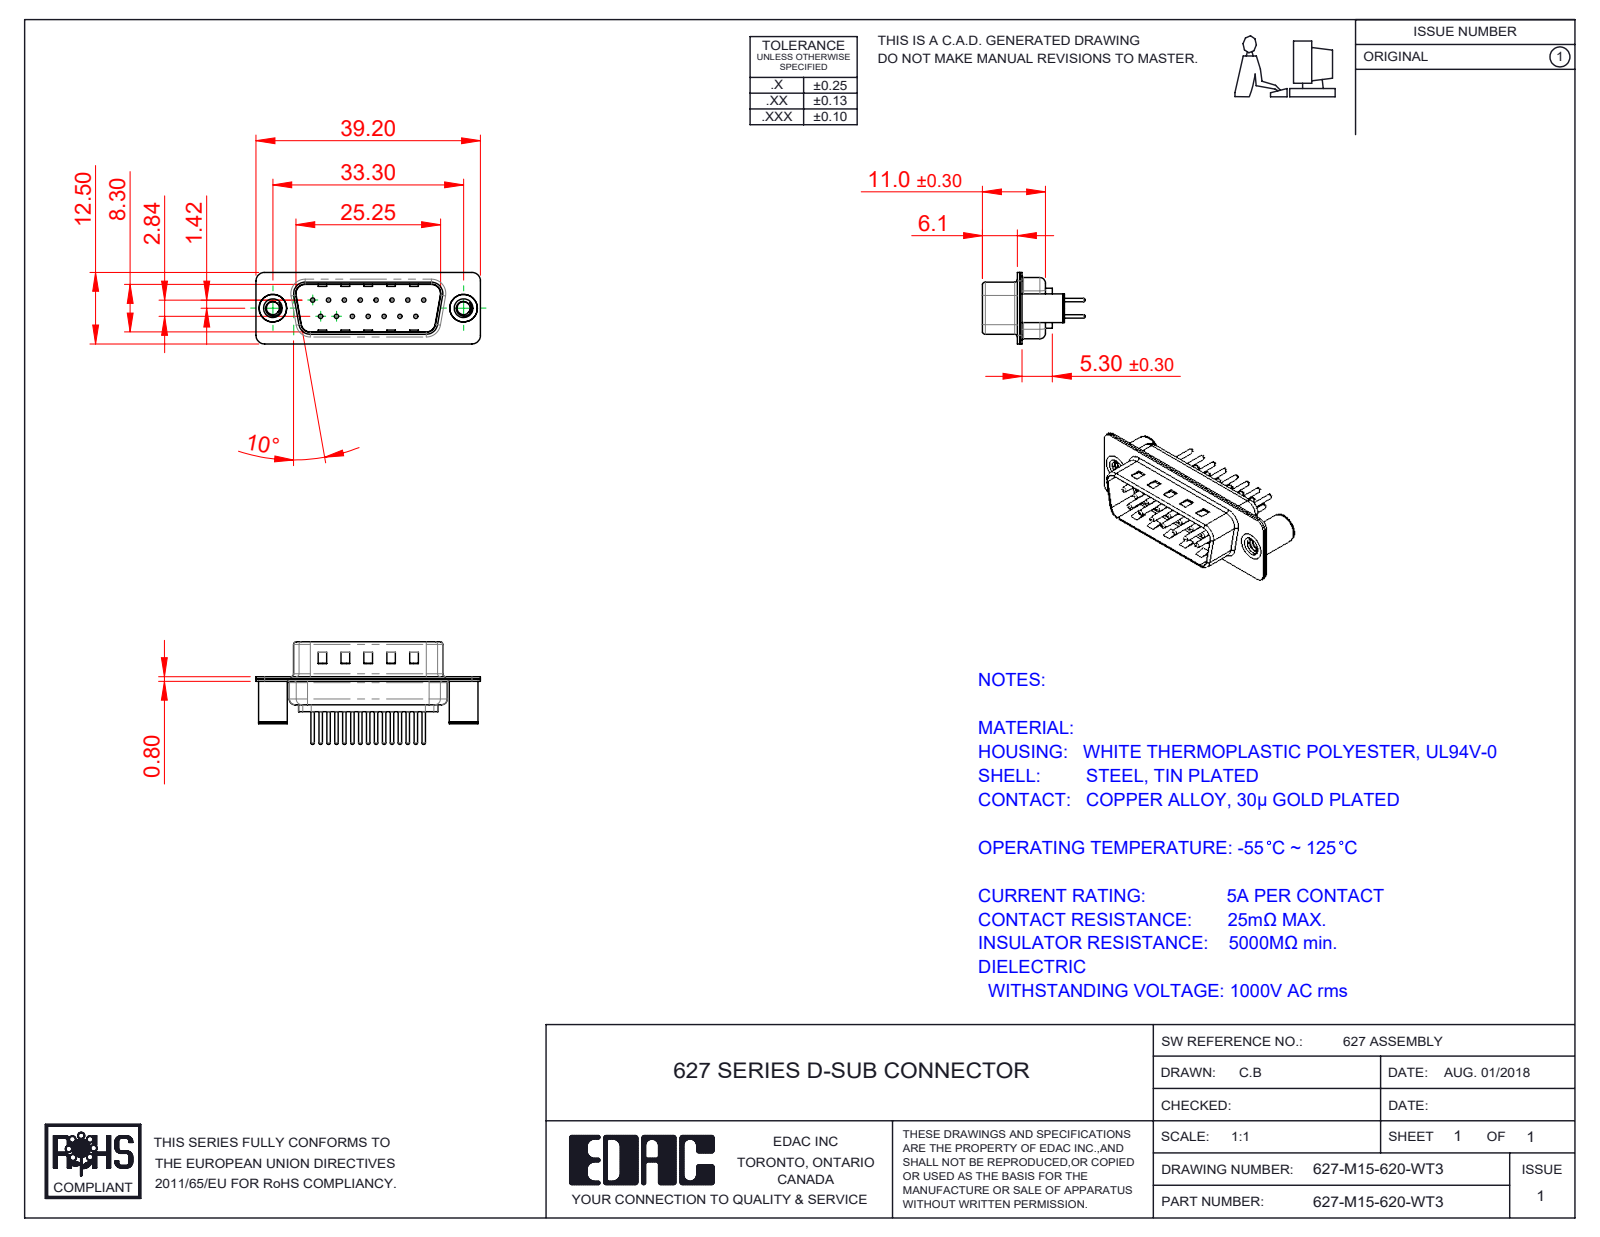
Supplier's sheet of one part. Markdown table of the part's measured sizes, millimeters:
| quantity | value |
| --- | --- |
| part name | 627M Contact Row 2_20; 627-M15-620-WT3; 627M Shell Front_15 Contacts; 627M Contact Row 1_20 (+3 more) |
| STEP written by | SolidWorks 2020 (CONFIG_CONTROL_DESIGN) |
| units | millimeters |
| bodies | 20 solids, 929 faces (244 planar, 367 cylindrical, 318 other) |
| overall size | 39.2 × 17.9 × 12.5 |
| volume | 1 966 mm³ |
| surface area | 5 067 mm² |
| round holes (diameter × count) | 0.75 × 15, 1.6 × 15, 2 × 15, 2.26 × 2, 3.26 × 2, 4 × 2, 4.8 × 2 |
| round bosses / shafts (diameter × count) | 1.5 × 15, 0.6 × 15, 5 × 2, 4.9 × 2 |
| partial cylindrical surfaces (radius × count) | 1.5 × 16, 2 × 12, 0.5 × 8, 1.6 × 8, 0.25 × 4, 0.6 × 4, 0.65 × 4, 0.9 × 4 |
| main face-to-face distances | 0.4, 0.8, 9.5, 9.1, 8.7, 9.9, 1.2, 5.3, 6.1, 5.7 |
| hole center spacings | 3.16, 2.77, 5.54, 8.31, 11.08, 5.03, 5.04, 7.48 |
